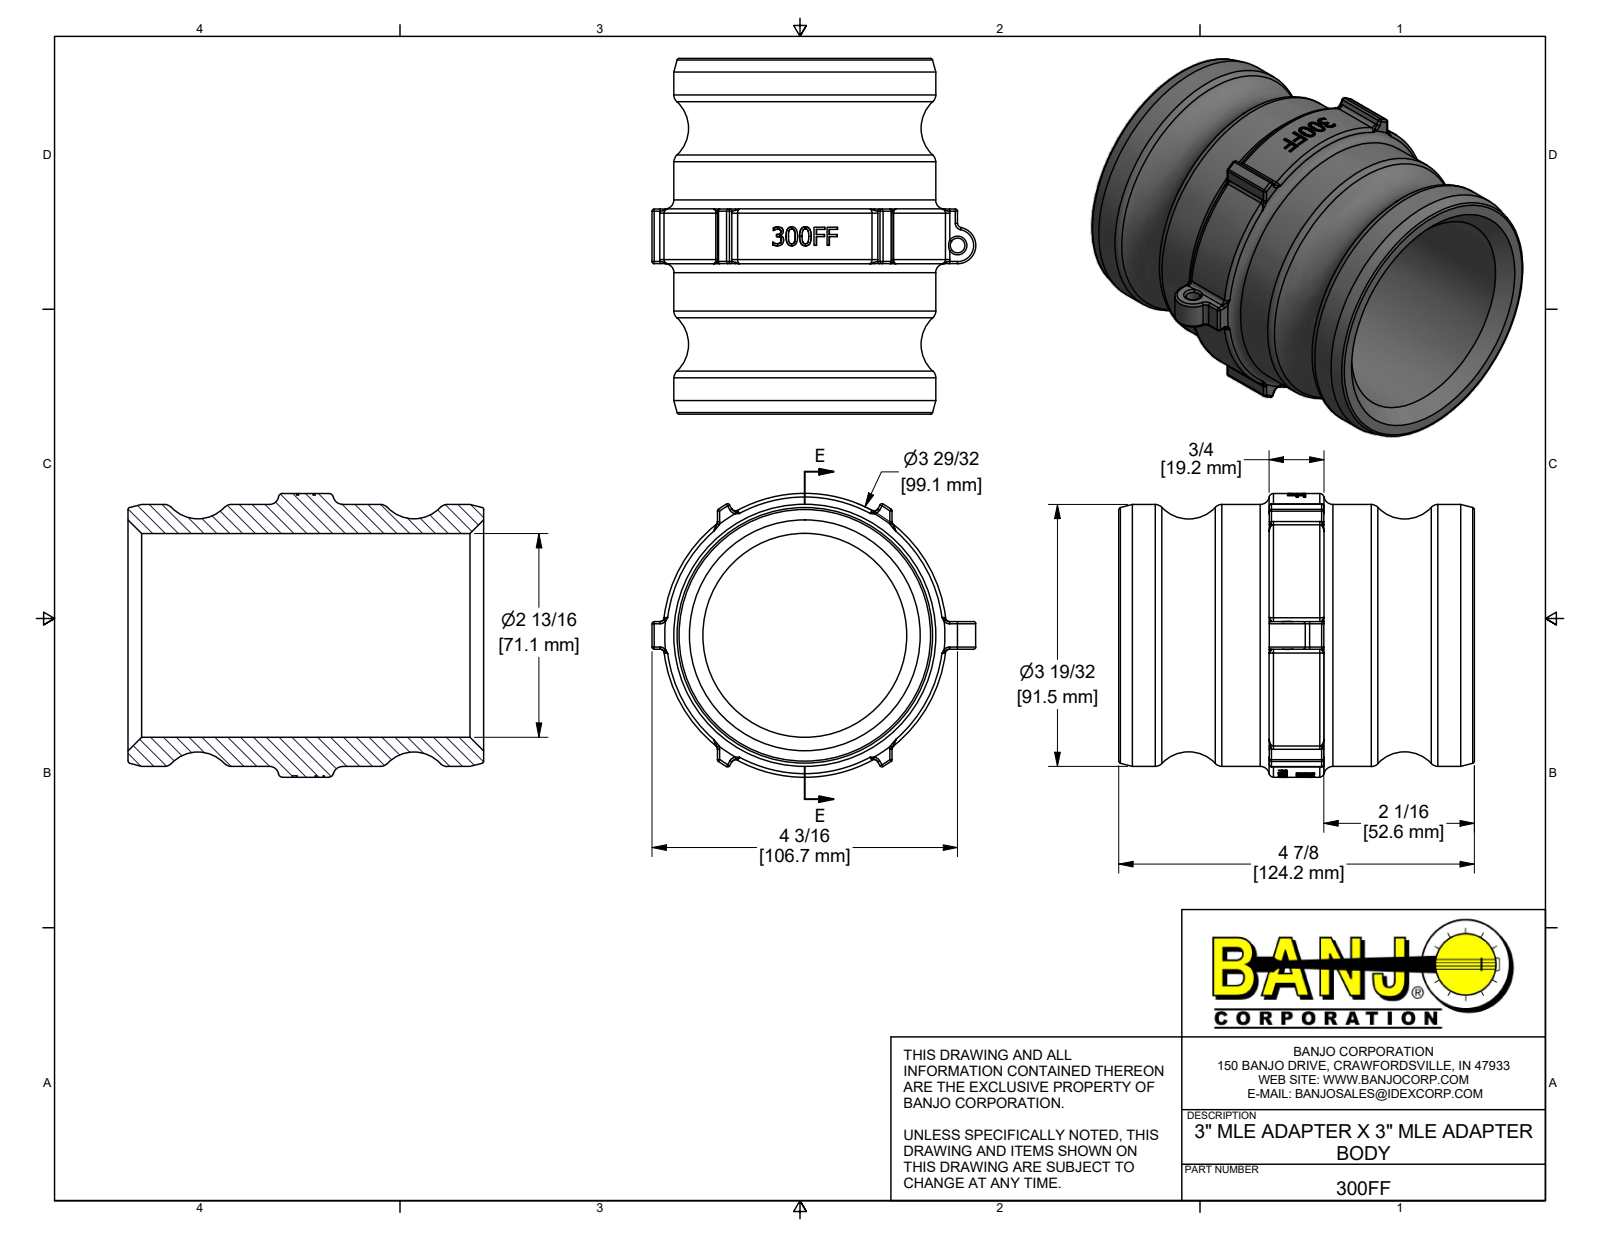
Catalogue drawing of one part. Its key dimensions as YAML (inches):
part_name: "300FF"
step_written_by: "Autodesk Inventor 2019 (AUTOMOTIVE_DESIGN)"
units: inches
bodies: {solids: 1, faces: 568, planar: 173, cylindrical: 104, other: 291}
overall_size: [4.89, 4.45, 3.9]
volume: 18.44
surface_area: 109.2
round_holes:
  - {diameter: 0.2, count: 1}
  - {diameter: 2.8, count: 1}
round_bosses_or_shafts:
  - {diameter: 3.9, count: 1}
  - {diameter: 3.602, count: 1}
partial_cylinders:
  - {radius: 0.03, count: 31}
  - {radius: 0.06, count: 13}
  - {radius: 0.25, count: 1}
  - {radius: 1.93, count: 1}
  - {radius: 2.1, count: 1}
face_to_face_distances: [4.89, 2.07, 2.82, 0.9, 3.3, 0.75, 2.4, 0.38, 4.2, 0.25]
